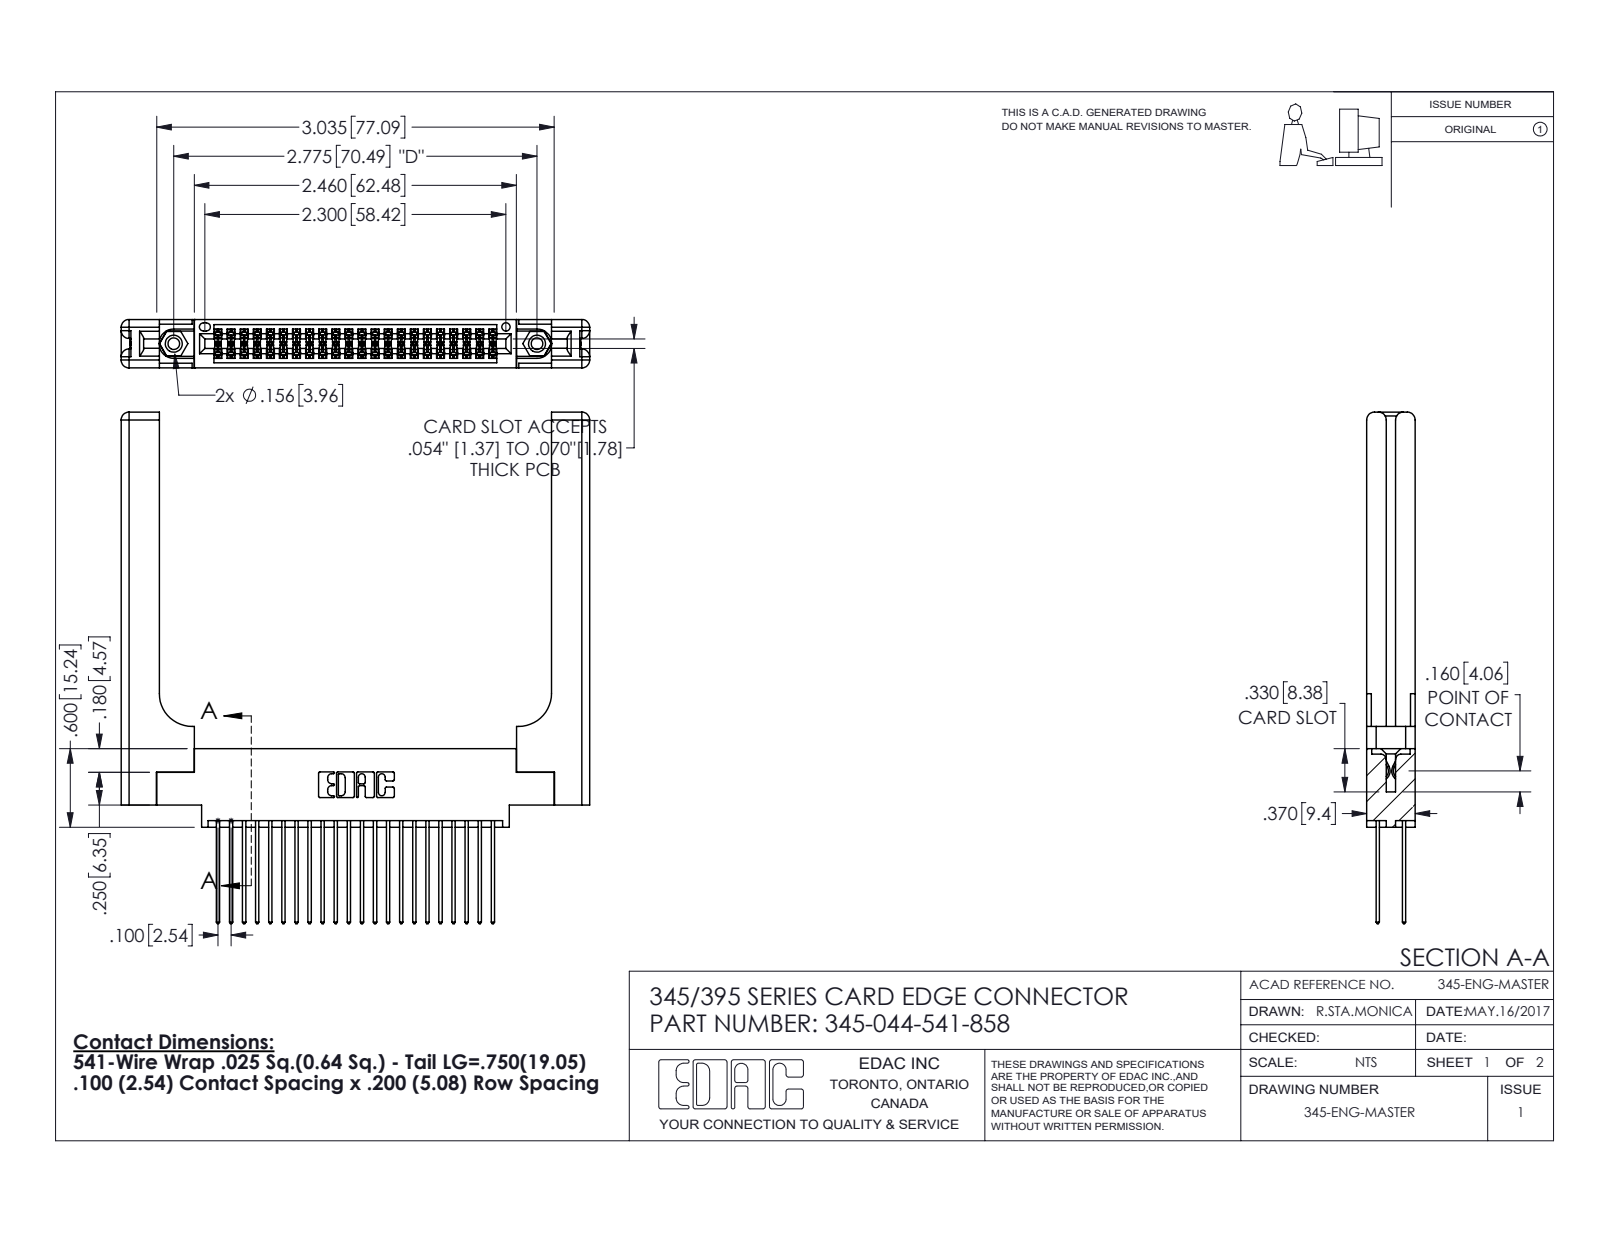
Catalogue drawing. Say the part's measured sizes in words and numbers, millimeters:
The part is named "345 Part_0.170 Offset - 0.156 Dia-TH; 345-220-058_345-220-058; 345-044-541-858; 345-250-001_345-250-001-102 (+1 more)". Its 3-D file was written by "SolidWorks 2016 (CONFIG_CONTROL_DESIGN)". It is 49 solids with 2586 faces: 1684 planar, 842 cylindrical and 60 other. Overall it measures 99.2 by 90.9 by 9.4 millimeters. Its volume is 17 260 cubic millimeters and its surface area 18 990 square millimeters. Round holes: 2 of diameter 2.3, 2 of diameter 3.2, 2 of diameter 4, 1 of diameter 1.6. Round bosses or shafts: 2 of diameter 3.9. Partial cylindrical surfaces (rounded edges, fillets, slot ends): 66 of radius 0.2, 44 of radius 0.3, 22 of radius 0.3, 16 of radius 1.5, 6 of radius 0.2, 6 of radius 0.8, 3 of radius 0.7, 2 of radius 0.4. The main face-to-face distances are 9.4, 1.8, 7.6, 2.5, 6.9, 0.6, 5.1, 5.7, 3.8, 3.8. The hole center spacings are 6.9, 64.5, 70.5.
